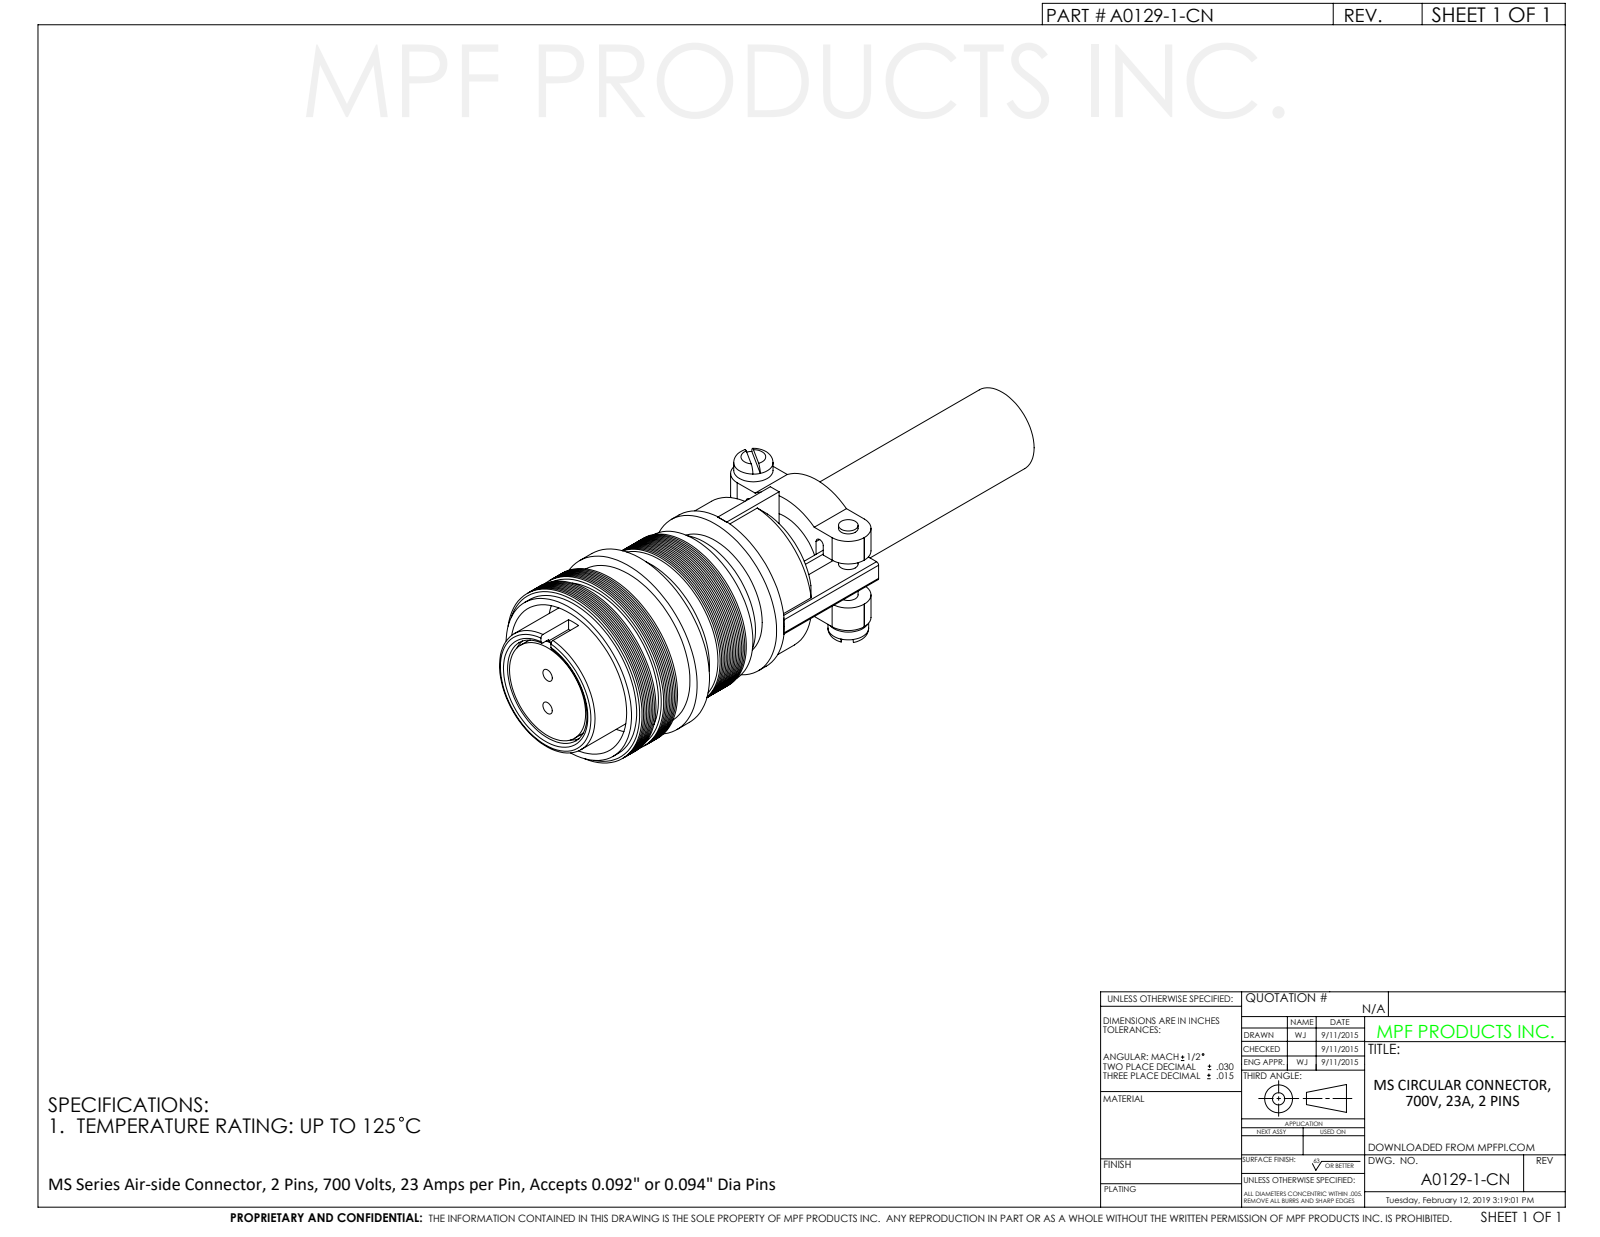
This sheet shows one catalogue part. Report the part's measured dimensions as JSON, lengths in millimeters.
{"part_name": "A0129-1-CN", "step_written_by": "SolidWorks 2012 (CONFIG_CONTROL_DESIGN)", "units": "millimeters", "bodies": {"solids": 1, "faces": 370, "planar": 105, "cylindrical": 83, "other": 182}, "overall_size": [112.7, 34, 34], "volume_mm3": 39230, "surface_area_mm2": 20230, "round_holes": [[2.3, 2], [14, 1], [19.8, 1], [28.6, 1]], "round_bosses_or_shafts": [[3.4, 2], [34, 1], [31.1, 1], [31, 1], [30.5, 1], [29, 1], [25.1, 1], [23.4, 1]], "partial_cylinders_radius": [[0.9, 8], [0.5, 4], [4, 4], [8.2, 1], [12, 1], [12, 1]], "face_to_face_distances": [30.3, 16.3, 11.9, 18.3, 2.5, 5.1, 53.2, 41.3, 23, 13.3], "hole_center_spacings": [6.9, 13.9]}
